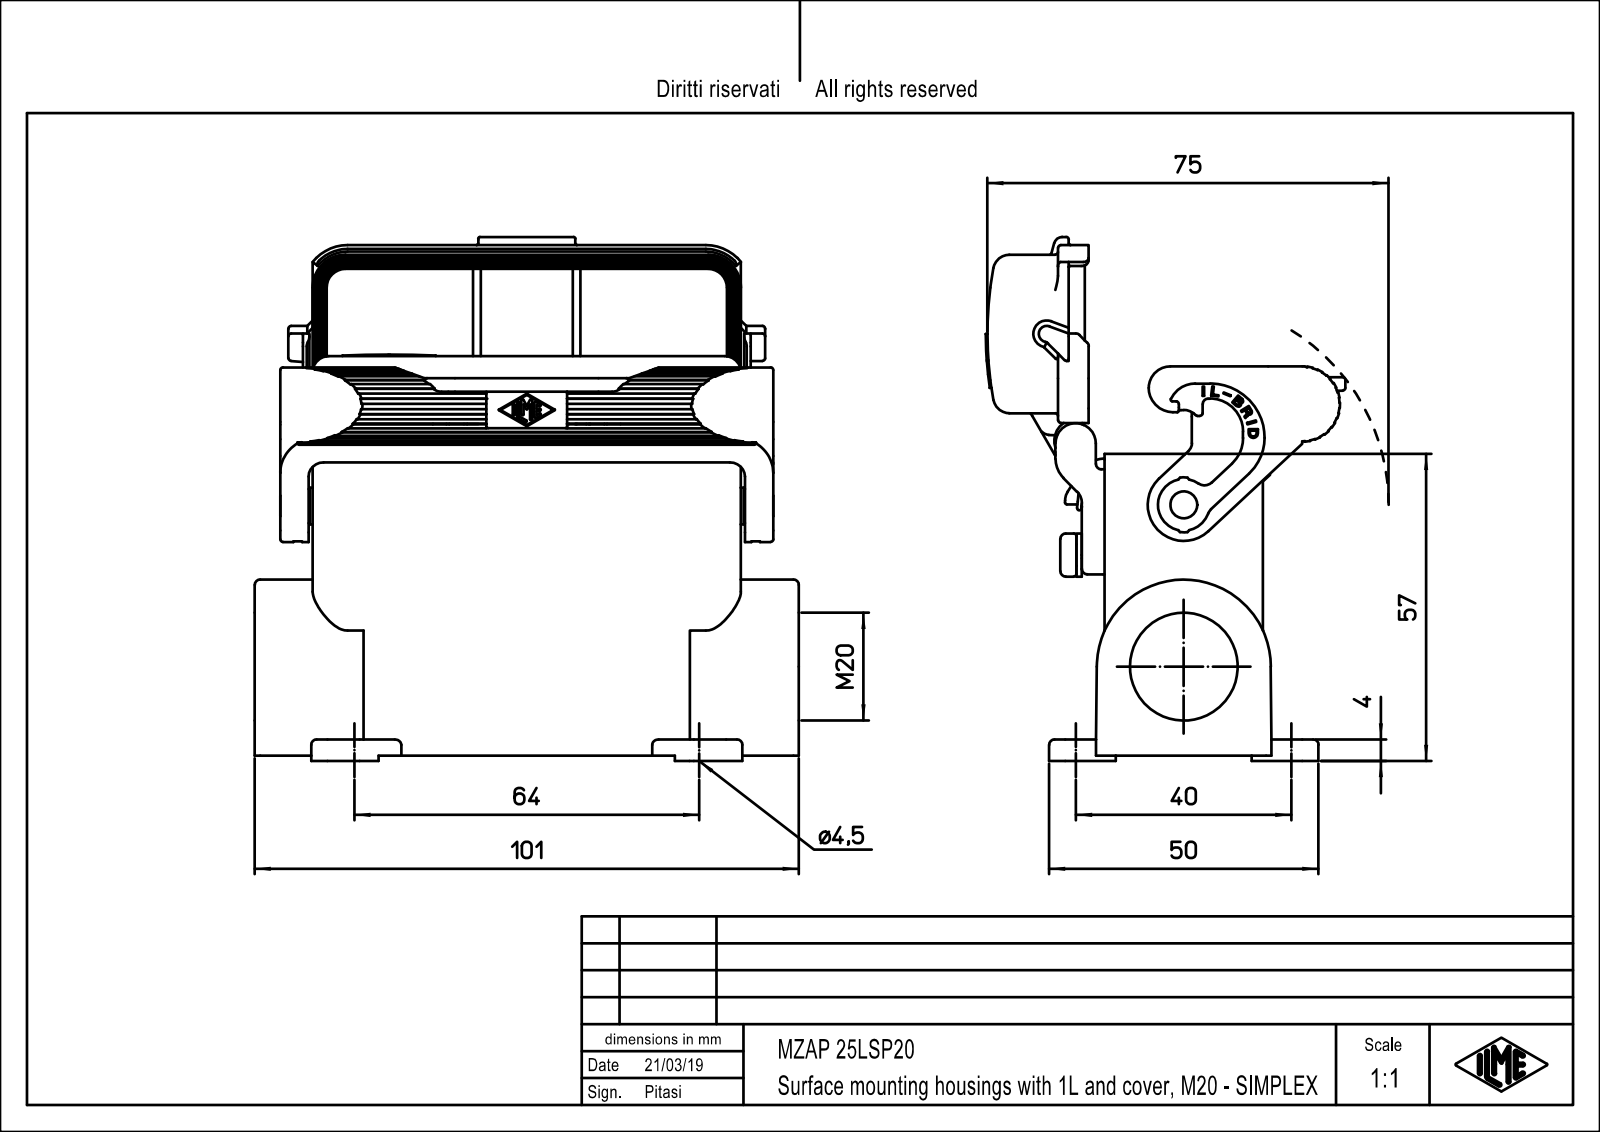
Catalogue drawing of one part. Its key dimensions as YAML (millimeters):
part_name: "MZAP_25_LSP20"
step_written_by: "PTC Creo Elements/Direct Modeling 19.0E 27-Jun-2016 (C) Parametric Technology GmbH (AUTOMOTIVE_DESIGN)"
units: millimeters
bodies: {solids: 1, faces: 537, planar: 293, cylindrical: 214, other: 30}
overall_size: [101, 97.03, 66.47]
volume: 95705
surface_area: 55472
round_holes:
  - {diameter: 3, count: 4}
  - {diameter: 4.5, count: 4}
  - {diameter: 18, count: 1}
  - {diameter: 20, count: 1}
round_bosses_or_shafts:
  - {diameter: 0.8, count: 3}
  - {diameter: 8.4, count: 1}
  - {diameter: 8, count: 1}
  - {diameter: 6.8, count: 1}
  - {diameter: 4.8, count: 1}
  - {diameter: 2.4, count: 1}
partial_cylinders:
  - {radius: 3, count: 13}
  - {radius: 3.5, count: 12}
  - {radius: 0.5, count: 7}
  - {radius: 6.5, count: 7}
  - {radius: 1.5, count: 4}
  - {radius: 2, count: 4}
  - {radius: 3.2, count: 4}
  - {radius: 3.4, count: 4}
face_to_face_distances: [2.76, 29.4, 26.65, 23.89, 2.75, 26.64, 3, 2.6, 26.8, 30.45]
hole_center_spacings: [12.04, 28.02, 66.1, 70.77, 16, 40, 64, 66]
